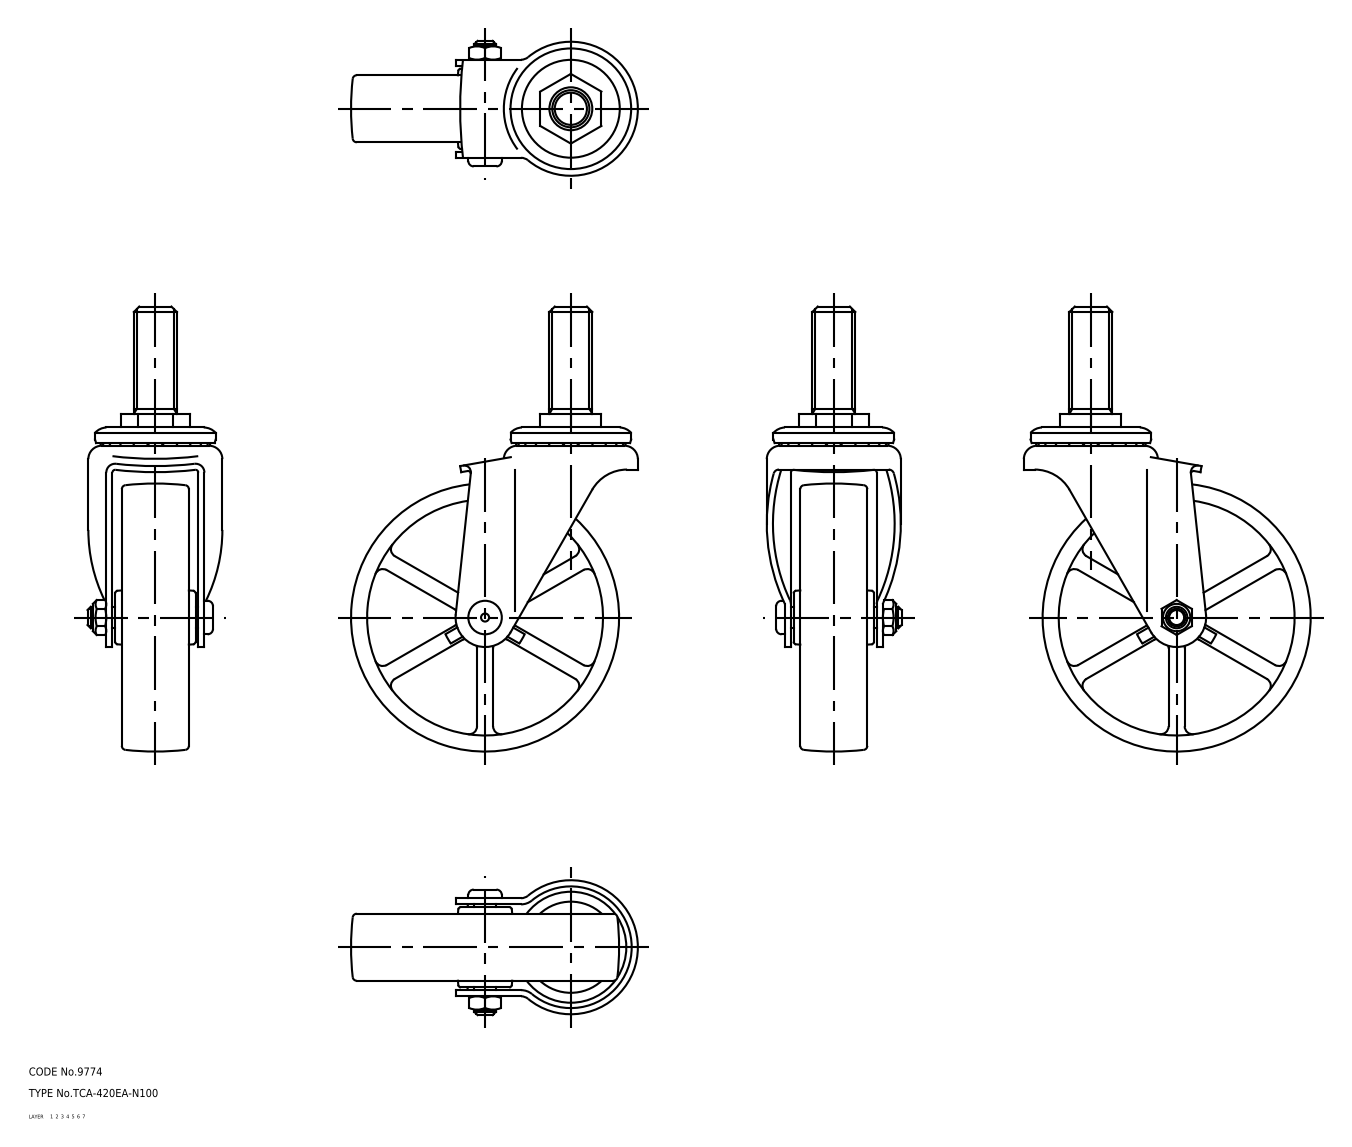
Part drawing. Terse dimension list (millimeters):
name: wheel; mounting plate; main shaft; axle (+1 more)
written by: CADfix (AUTOMOTIVE_DESIGN)
unit: mm
bodies: 5 solids, 592 faces (0 planar, 0 cylindrical, 592 other)
size: 166 × 107 × 50.3
volume: 187 555 mm³; area: 56 151 mm²
